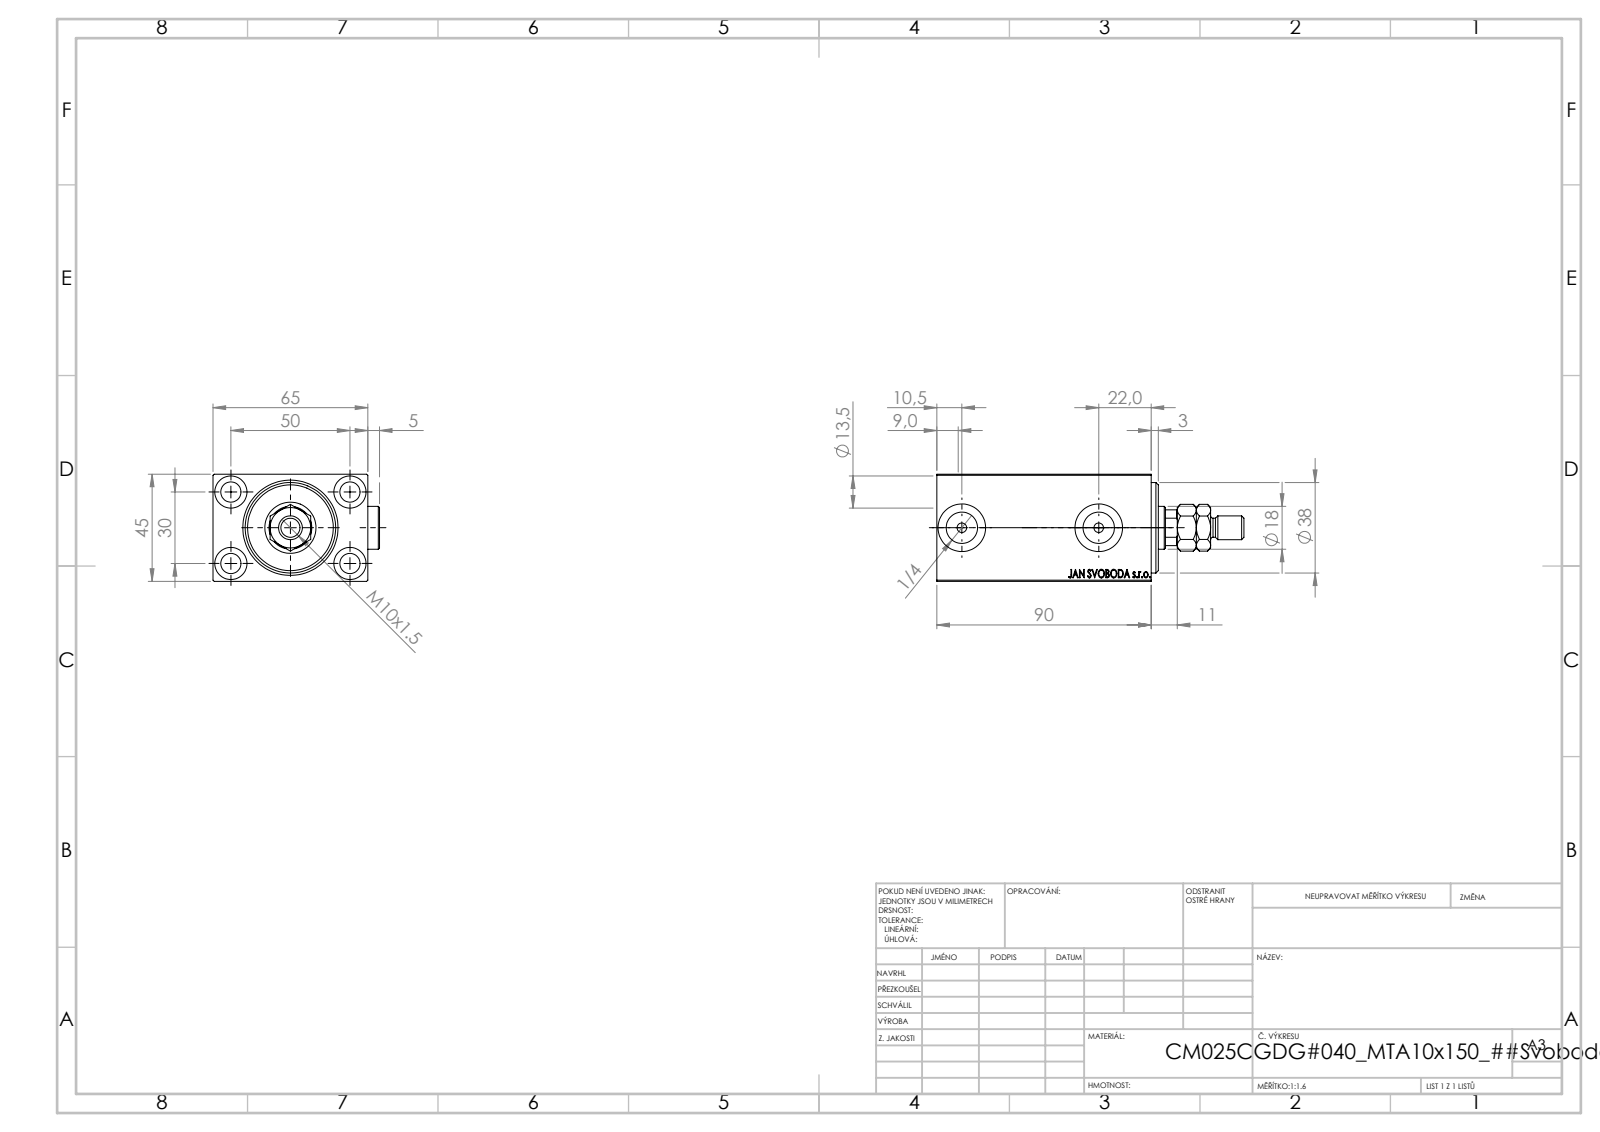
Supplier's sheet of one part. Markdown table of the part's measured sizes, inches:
| quantity | value |
| --- | --- |
| part name | Zatka_OIL_PORT; MTA; V450CM_VC_B; V450CM_C_Body (+1 more) |
| STEP written by | SolidWorks 2019 (CONFIG_CONTROL_DESIGN) |
| units | inches |
| bodies | 6 solids, 965 faces (457 planar, 80 cylindrical, 428 other) |
| overall size | 5.079 × 2.752 × 1.772 |
| volume | 14.06 in³ |
| surface area | 92.98 in² |
| round holes (diameter × count) | 0.335 × 5, 0.531 × 4, 0.157 × 2, 0.518 × 2, 0.787 × 2, 0.709 × 1, 0.846 × 1, 0.984 × 1, 1.063 × 1, 1.496 × 1 |
| round bosses / shafts (diameter × count) | 0.709 × 2, 0.394 × 1, 0.315 × 1 |
| partial cylindrical surfaces (radius × count) | 0.335 × 1 |
| main face-to-face distances | 1.772, 2.559, 0.197, 0.236, 3.11, 3.307, 2.555, 3.543, 3.346, 0.118 |
| hole center spacings | 1.148, 1.181, 1.969, 2.296, 2.264 |
